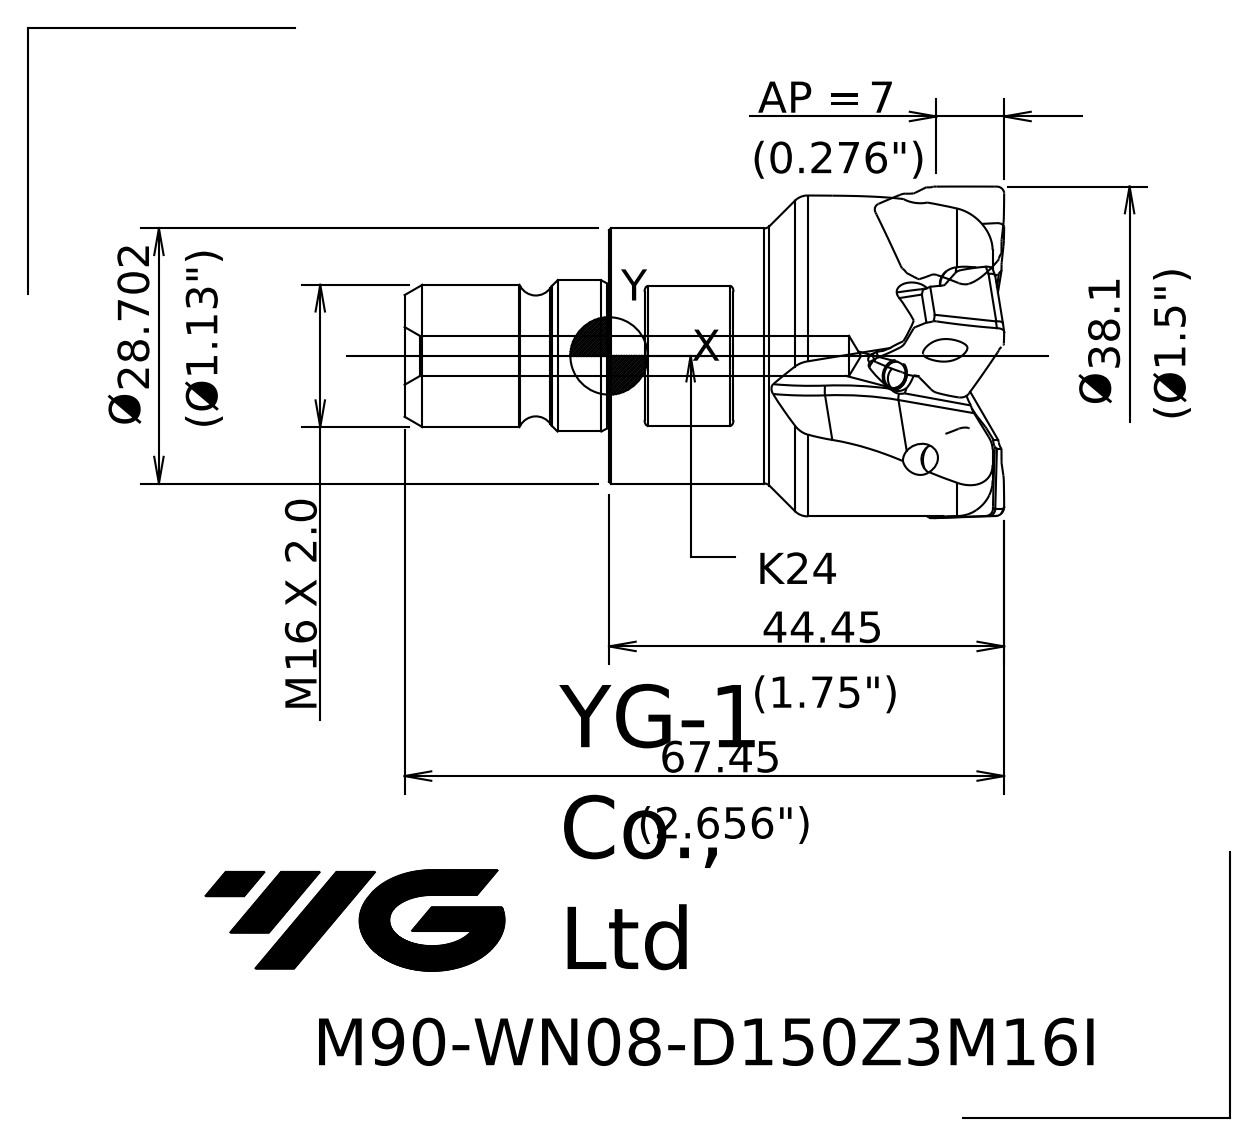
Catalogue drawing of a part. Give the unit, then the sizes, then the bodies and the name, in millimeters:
Units: millimetres
Overall size (bounding box): 67.45 × 38.12 × 38.12
Round holes (diameter × count): ⌀2 ×1, ⌀4.5 ×1
Round bosses / shafts (diameter × count): ⌀36.1 ×1, ⌀28.7 ×1, ⌀17 ×1, ⌀16 ×1
Partial cylindrical surfaces — rounded edges, fillets, slot ends (radius × count): R0.4 ×4
Main face-to-face distances: 43.15, 24, 66.15, 23, 3.6, 39.55, 62.55, 29.15, 25.55, 14
Volume: 38 791 mm³ · Surface area: 11 841 mm²
Bodies: 1 solid, 80 faces (10 planar, 10 cylindrical, 60 other)
Part name (STEP PRODUCT): 1022928893103xcb
STEP written by: SIEMENS PLM Software NX 10.0 (AP203_CONFIGURATION_CONTROLLED_3D_DESIGN_OF_MECHANICAL_PARTS_AND_ASSEMBLIES_MIM_LF)
